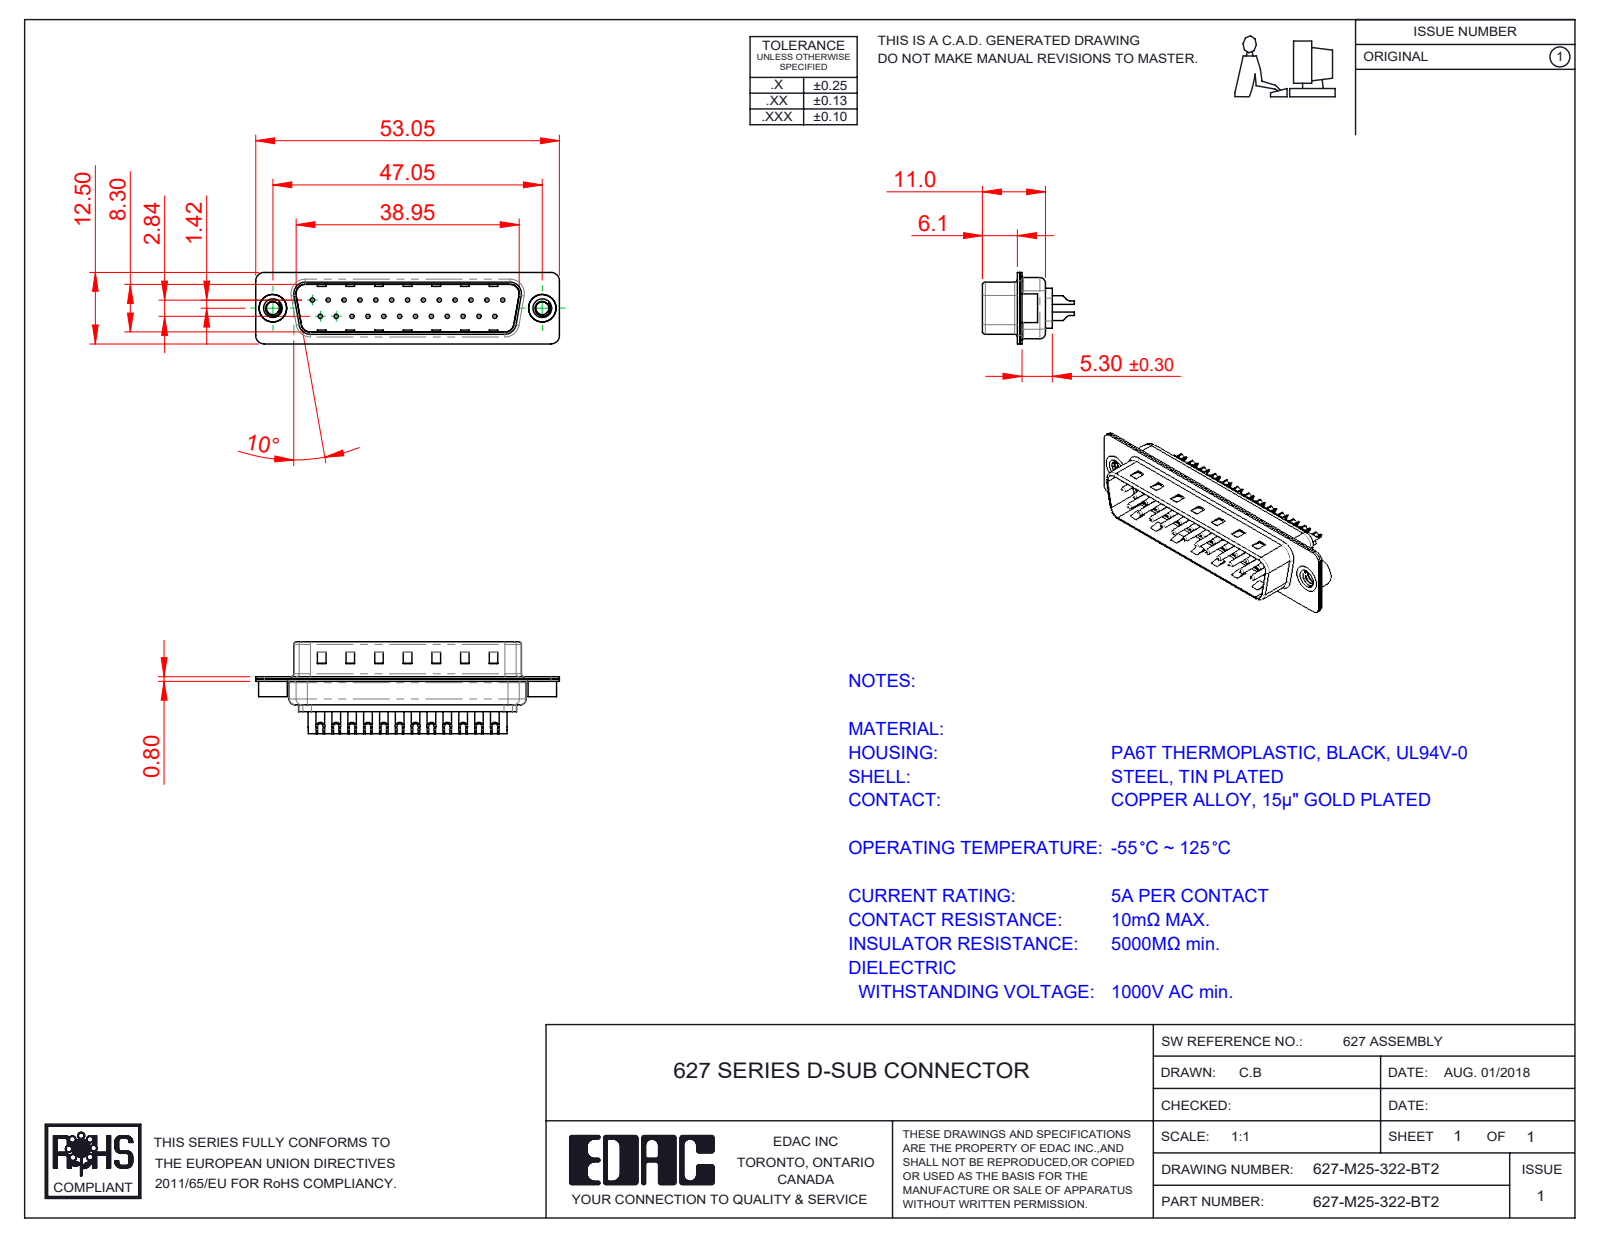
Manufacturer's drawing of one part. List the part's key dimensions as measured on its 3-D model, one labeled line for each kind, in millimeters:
Part name (STEP PRODUCT): 627M Contact Row 2_22; 627M Housing_25 Contacts; 627M Shell Rear_25 Contacts; 627M Contact Row 1_22 (+3 more)
STEP written by: SolidWorks 2020 (CONFIG_CONTROL_DESIGN)
Units: millimetres
Bodies: 30 solids, 1301 faces (396 planar, 537 cylindrical, 368 other)
Overall size (bounding box): 53.05 × 16.05 × 12.5
Volume: 2 776 mm³ · Surface area: 7 078 mm²
Round holes (diameter × count): ⌀0.75 ×25, ⌀1 ×25, ⌀1.6 ×25, ⌀2 ×25, ⌀2.26 ×2, ⌀4 ×2, ⌀4.8 ×2
Round bosses / shafts (diameter × count): ⌀1.5 ×25, ⌀5 ×2, ⌀4.9 ×2
Partial cylindrical surfaces — rounded edges, fillets, slot ends (radius × count): R1.5 ×16, R2 ×12, R0.5 ×8, R1.6 ×8, R1 ×6, R0.25 ×4, R0.6 ×4, R0.65 ×4
Main face-to-face distances: 0.4, 0.8, 9.5, 9.1, 8.7, 9.9, 1.2, 0.75, 0.35, 6.1
Hole centre spacings: 3.16, 2.77, 5.54, 8.31, 11.08, 13.85, 16.62, 5.03
